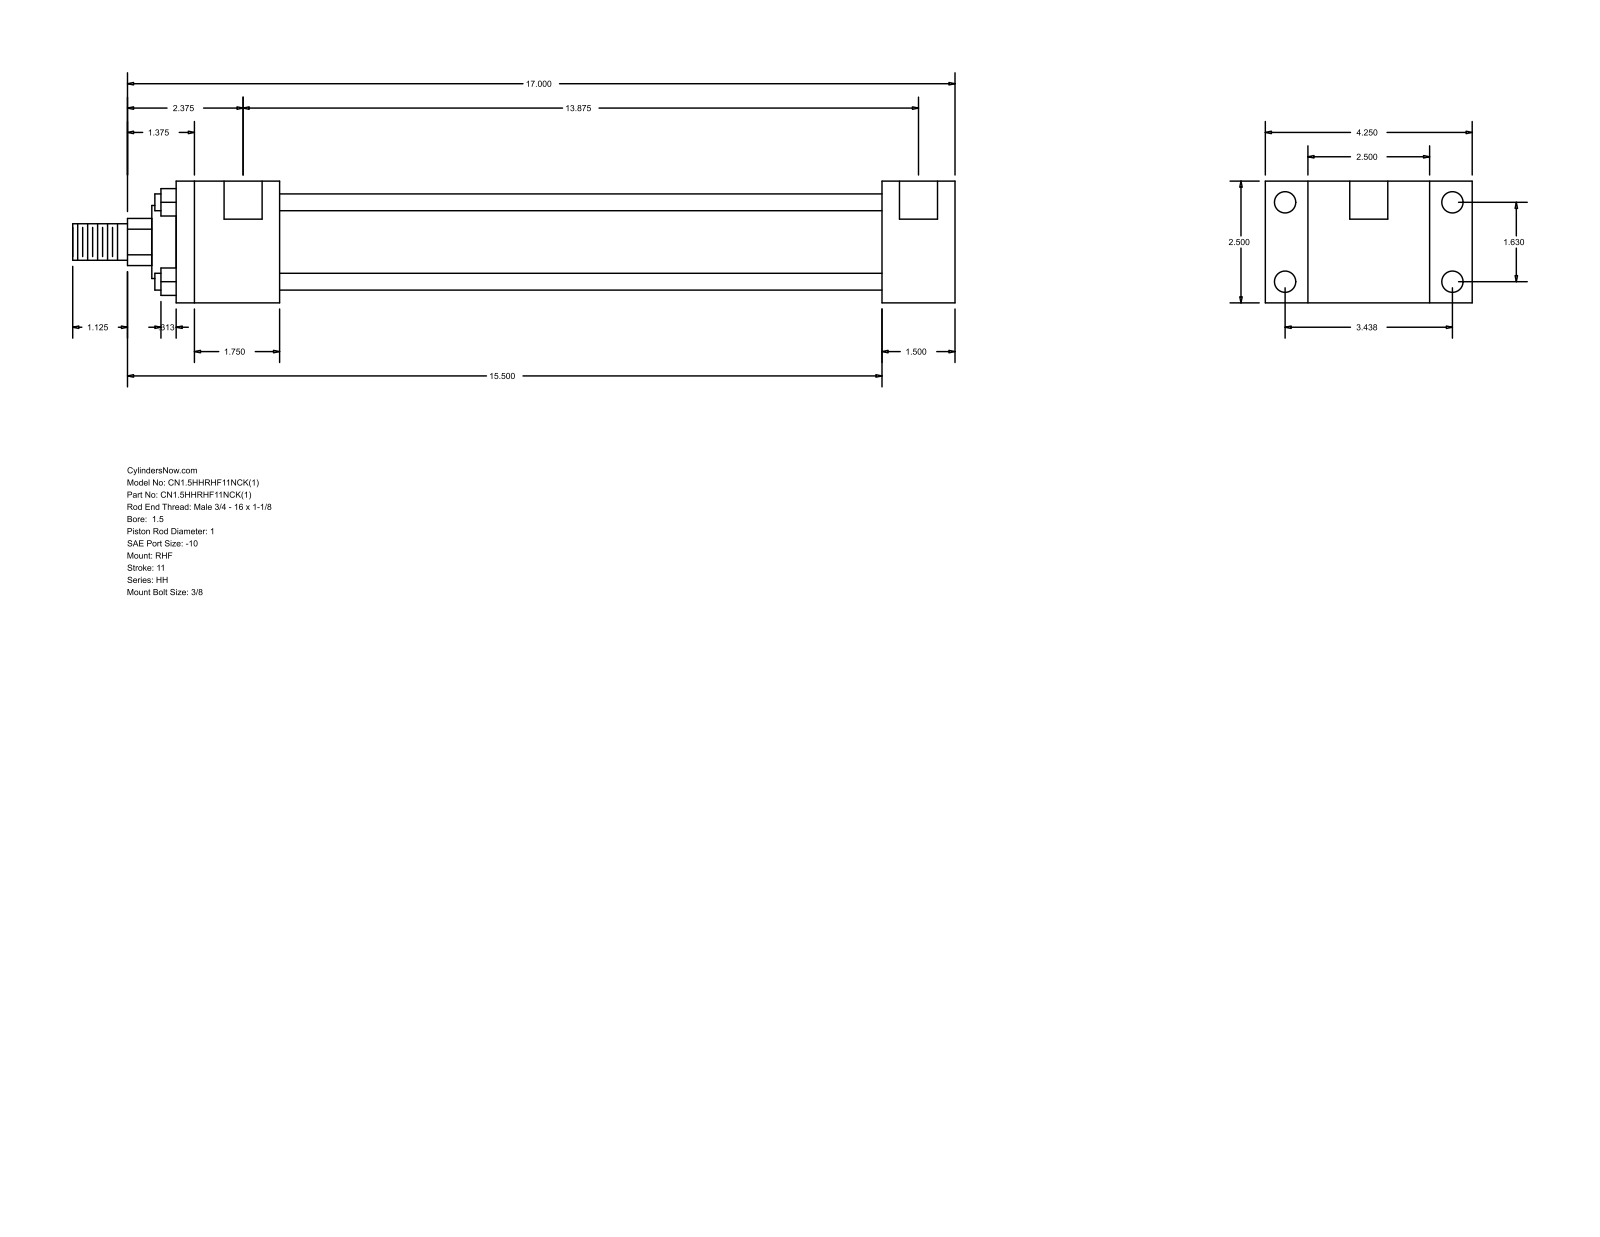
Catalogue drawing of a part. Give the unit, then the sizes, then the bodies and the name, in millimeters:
Units: millimetres
Overall size (bounding box): 460.38 × 107.95 × 63.5
Round holes (diameter × count): ⌀5.56 ×4, ⌀11.13 ×4, ⌀19.84 ×2
Round bosses / shafts (diameter × count): ⌀8.76 ×4, ⌀44.45 ×1, ⌀38.1 ×1, ⌀25.4 ×1, ⌀19.05 ×1
Partial cylindrical surfaces — rounded edges, fillets, slot ends (radius × count): R12.29 ×1
Main face-to-face distances: 63.5, 22.23, 85.73, 38.1, 107.96, 314.32, 352.42, 53.98, 368.3, 406.4
Hole centre spacings: 1.59, 41.4, 87.32, 96.64, 354.01, 355.6, 352.42
Bodies: 0 solids, 88 faces (60 planar, 28 cylindrical, 0 other)
Part name (STEP PRODUCT): HH_RHF__0150_1
STEP written by: GSSL Pune (CONFIG_CONTROL_DESIGN)
